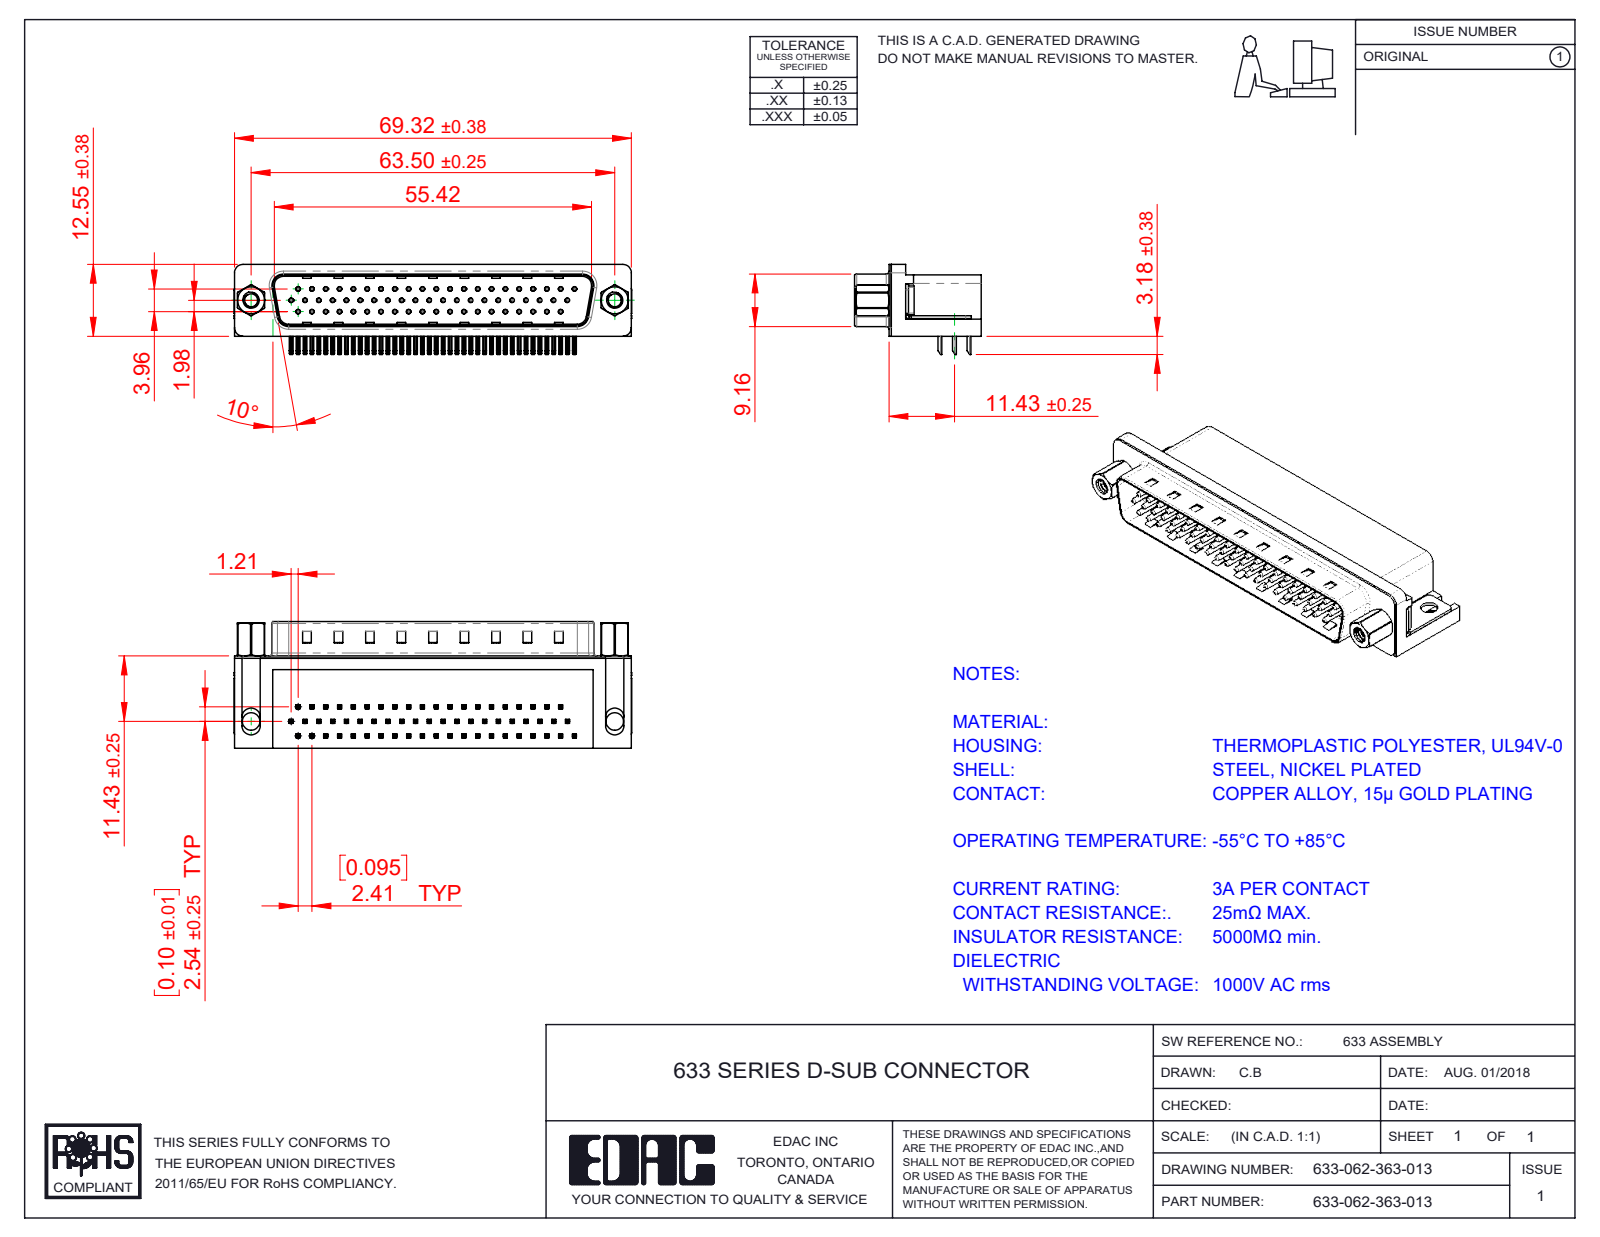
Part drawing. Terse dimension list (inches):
name: 633 Housing_62 Contact; 633 4-40 Hex Standoff; 633 4-40 Threaded Rivet; 633 Thru Hole Board Mount (+5 more)
written by: SolidWorks 2016 (CONFIG_CONTROL_DESIGN)
unit: in
bodies: 70 solids, 5194 faces (3233 planar, 1506 cylindrical, 455 other)
size: 2.732 × 0.87 × 0.619
volume: 0.687 in³; area: 21.46 in²
holes: 62× ⌀0.014, 62× ⌀0.031, 2× ⌀0.089, 2× ⌀0.09, 2× ⌀0.12, 2× ⌀0.157, 2× ⌀0.189, 2× ⌀0.197
bosses: 62× ⌀0.03, 2× ⌀0.193, 2× ⌀0.187, 2× ⌀0.154, 2× ⌀0.11
rounds: 256× R0.01, 124× R0.005, 16× R0.039, 9× R0.02, 8× R0.063, 7× R0.059, 4× R0.035, 4× R0.079
face distances: 0.016, 0.407, 0.618, 0.345, 0.114, 0.098, 0.1, 0.329, 0.634, 0.083
hole spacings: 0.095, 0.19, 0.285, 0.38, 0.57, 0.665, 0.19, 0.285
